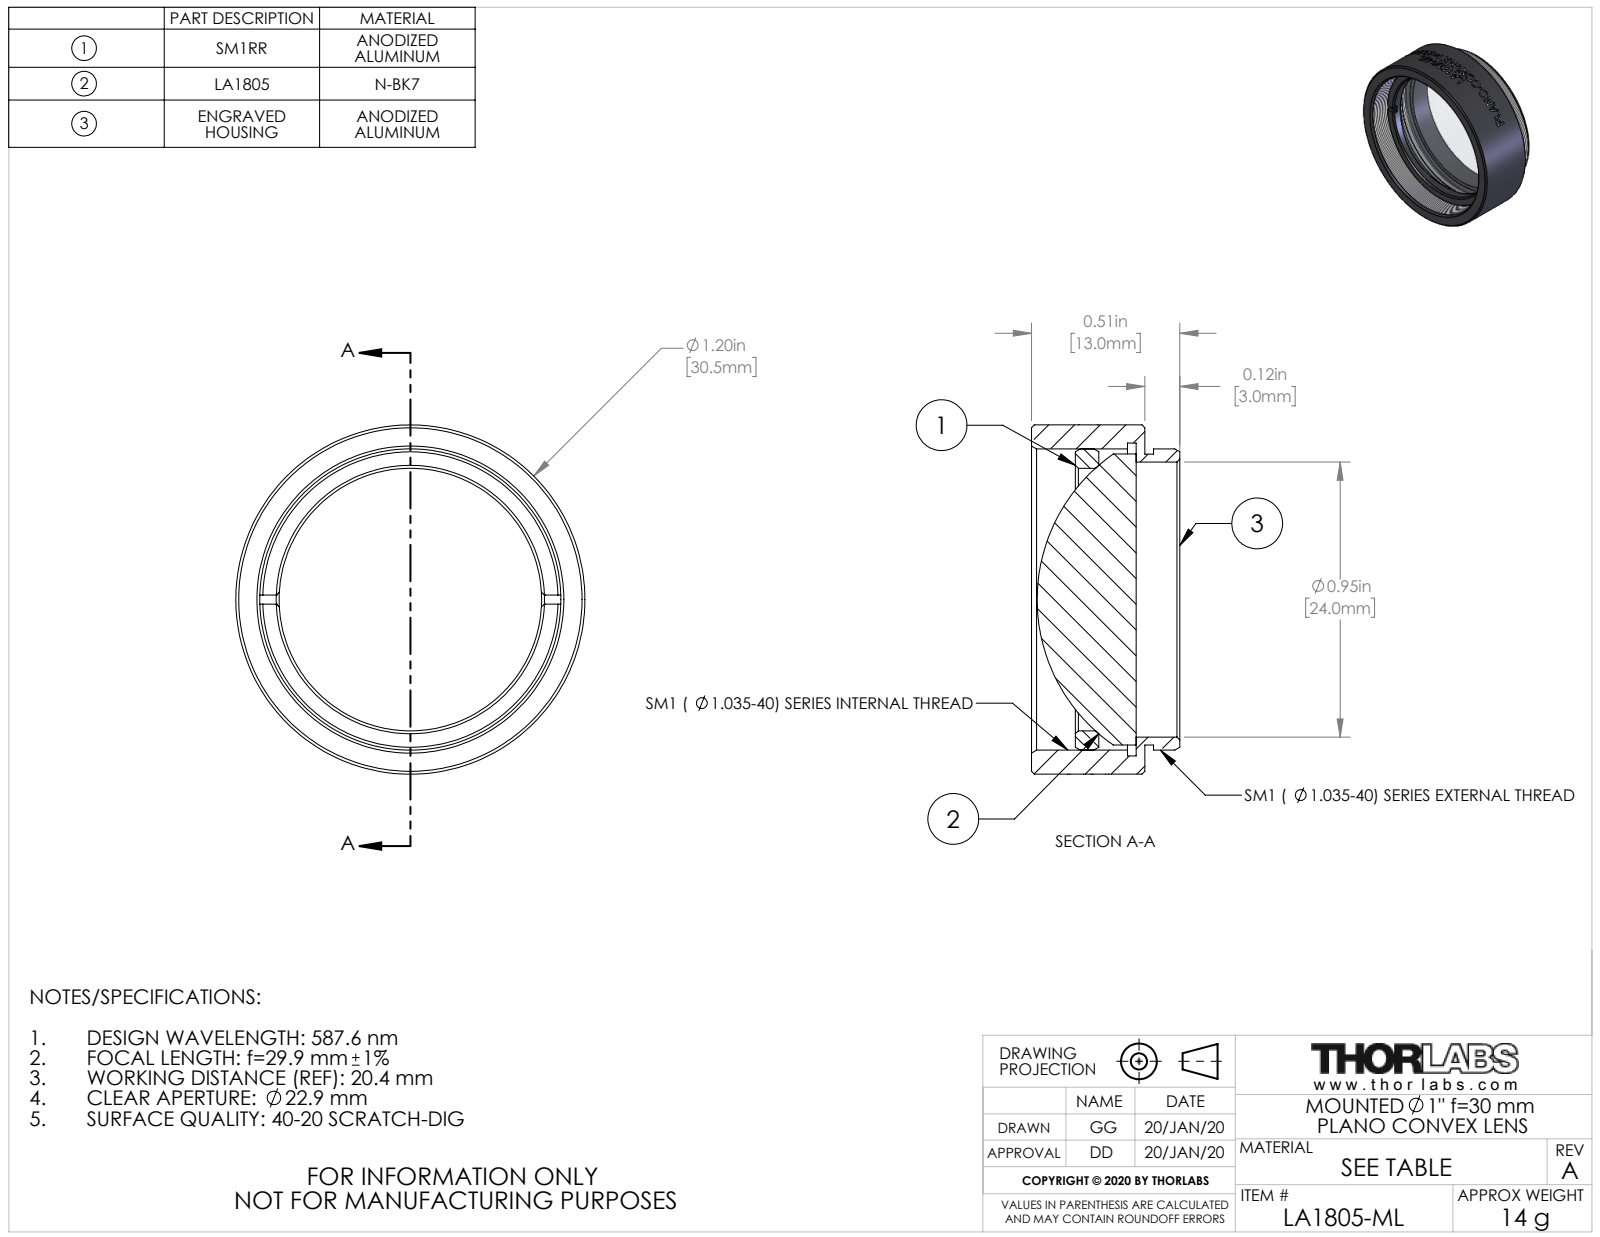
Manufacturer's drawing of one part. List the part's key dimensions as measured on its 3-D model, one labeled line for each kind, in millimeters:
Part name (STEP PRODUCT): TTN203732-E0W
STEP written by: SolidWorks 2018 (CONFIG_CONTROL_DESIGN)
Units: millimetres
Bodies: 3 solids, 121 faces (20 planar, 77 cylindrical, 24 other)
Overall size (bounding box): 30.48 × 30.48 × 12.95
Volume: 5 213 mm³ · Surface area: 4 722 mm²
Round holes (diameter × count): ⌀22.91 ×1, ⌀24 ×1, ⌀26.29 ×1, ⌀27.3 ×1
Round bosses / shafts (diameter × count): ⌀30.48 ×1, ⌀26.29 ×1, ⌀25.4 ×1, ⌀25.37 ×1
Main face-to-face distances: 0.76, 9.91, 9.15, 4.03, 3.27, 5.88, 6.06, 5.3, 2.03, 3.85
